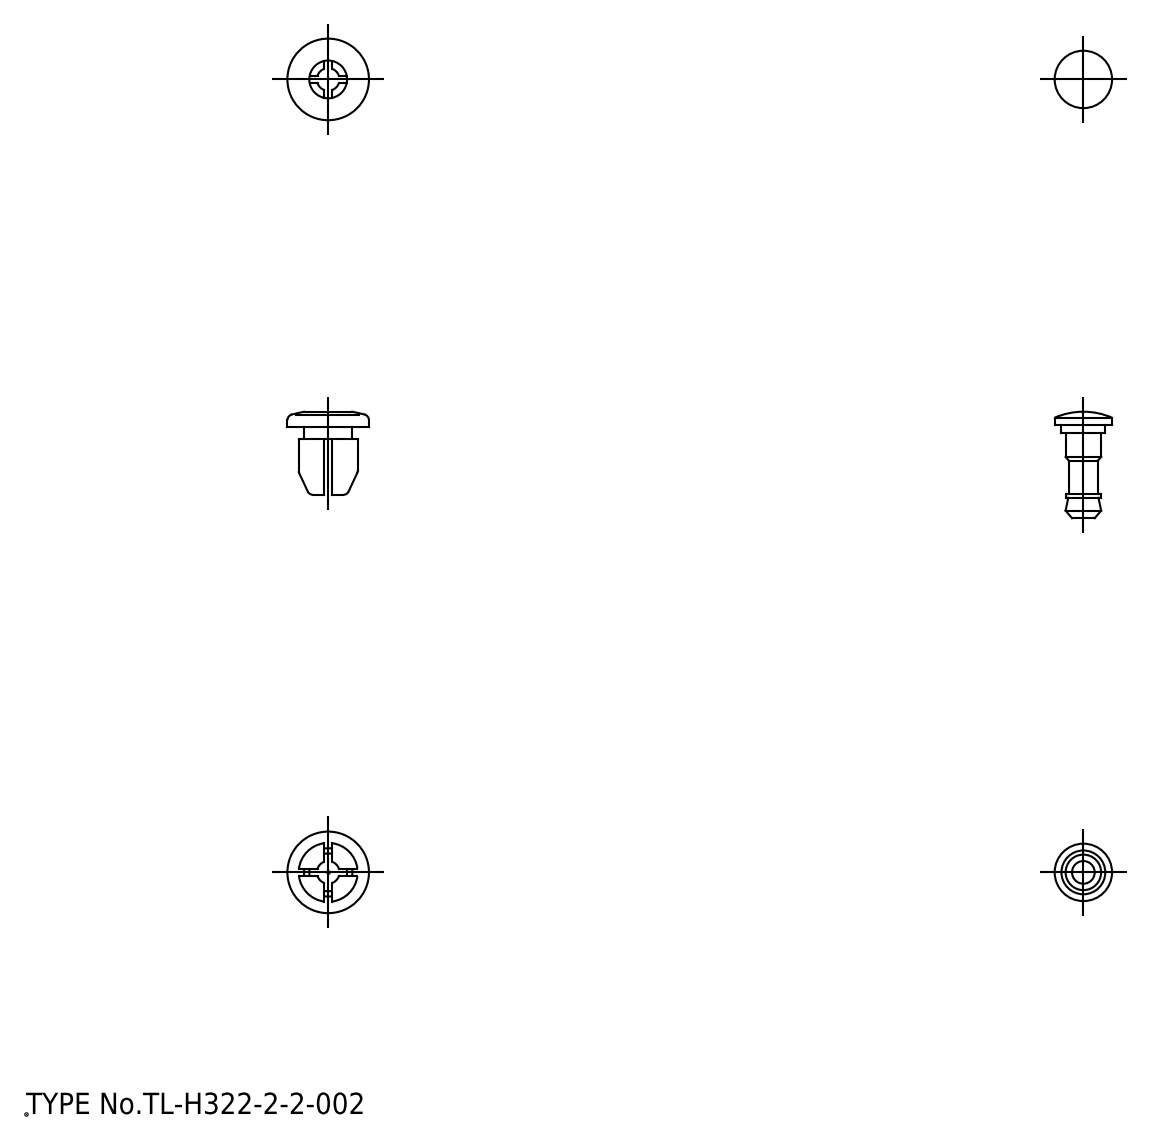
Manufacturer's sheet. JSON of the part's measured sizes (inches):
{"part_name": "grommet; plunger", "step_written_by": "spGate 18.9.1 (****-****-****-****) (AUTOMOTIVE_DESIGN)", "units": "inches", "bodies": {"solids": 2, "faces": 79, "planar": 31, "cylindrical": 24, "other": 24}, "overall_size": [0.61, 0.429, 0.429], "volume_in3": 0.033, "surface_area_in2": 1.38, "round_holes": [[0.197, 1]], "round_bosses_or_shafts": [[0.429, 1], [0.307, 1], [0.299, 1], [0.252, 1], [0.228, 1], [0.185, 1], [0.15, 1]], "partial_cylinders_radius": [[0.059, 1]], "face_to_face_distances": [0.039, 0.185, 0.106, 0.378, 0.063, 0.248, 0.236, 0.299, 0.484, 0.142]}
